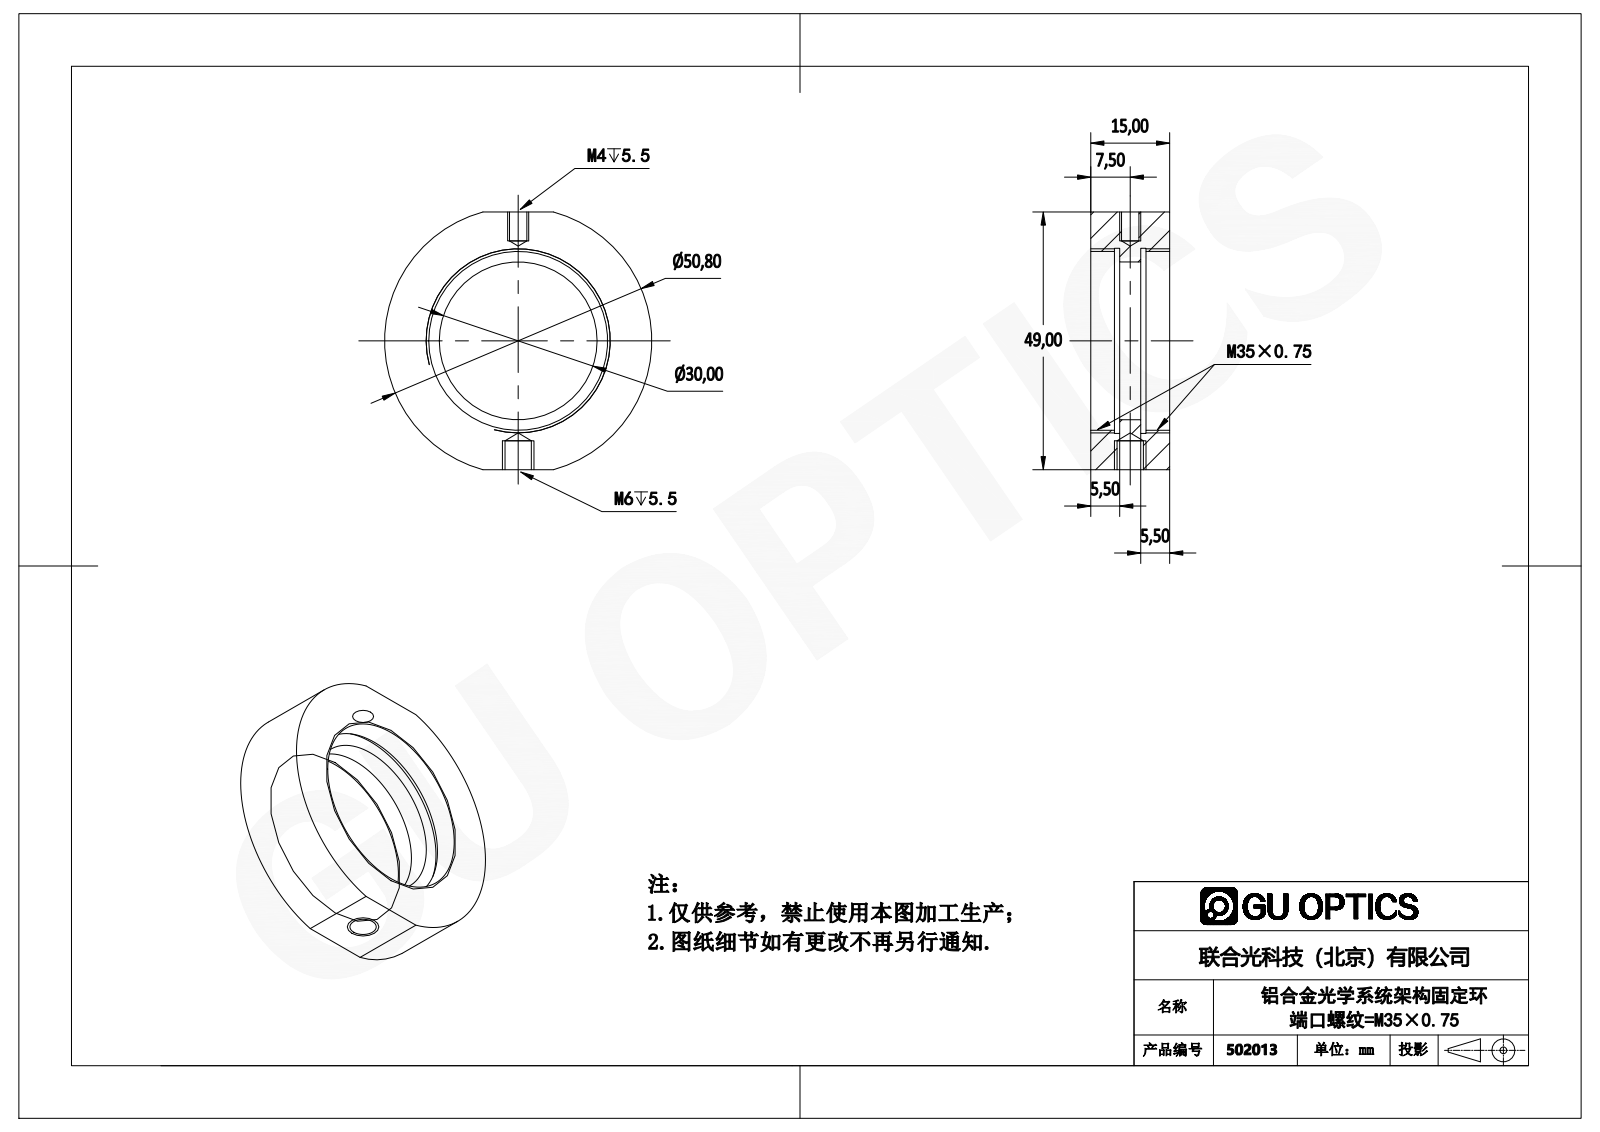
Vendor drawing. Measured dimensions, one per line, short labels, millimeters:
name: 502013
written by: SolidWorks 2016 (CONFIG_CONTROL_DESIGN)
unit: mm
bodies: 1 solid, 29 faces (8 planar, 17 cylindrical, 4 other)
size: 50.8 × 49 × 15
volume: 17 048 mm³; area: 6 965 mm²
holes: 1× ⌀3.3, 1× ⌀5, 1× ⌀30, 1× ⌀34, 1× ⌀35.2
bosses: 1× ⌀50.8
face distances: 15, 5.5, 9.5, 4, 49, 4.5, 10.5, 1, 5, 6
